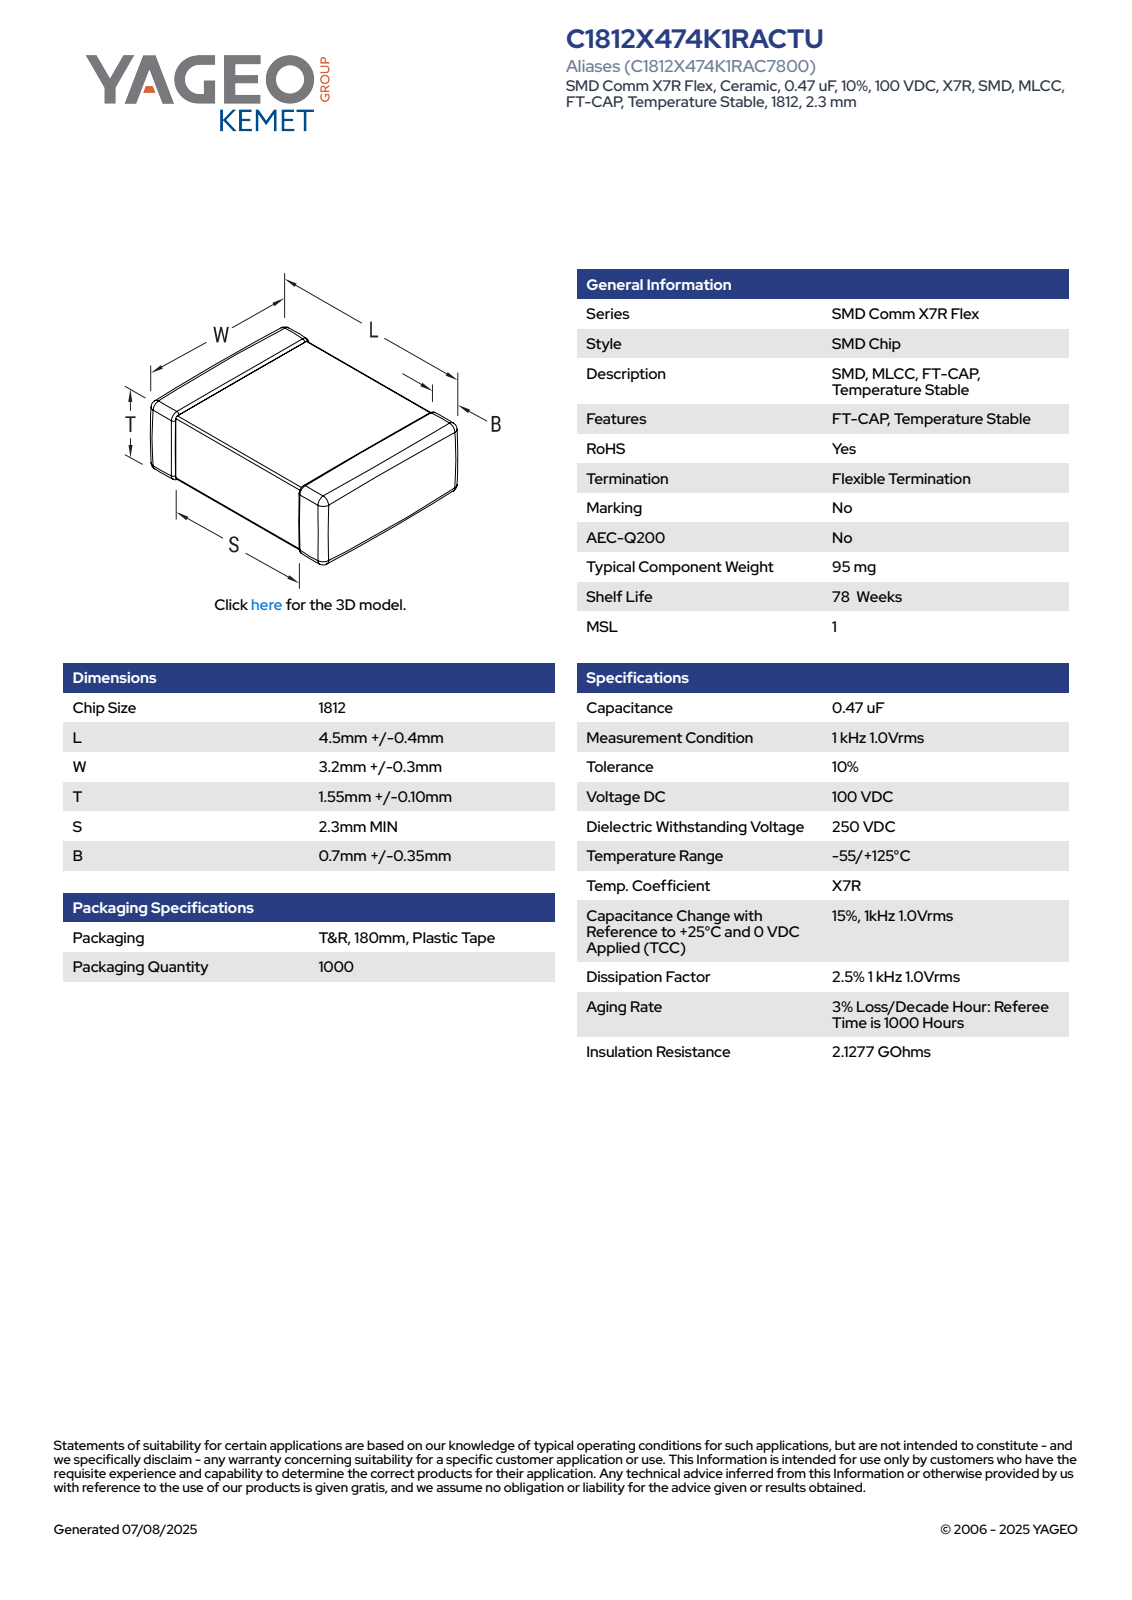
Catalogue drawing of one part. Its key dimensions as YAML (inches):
part_name: "CCS_CCSTD_1812_L4.9W3.5T1.65B0.7"
step_written_by: "SolidWorks 2021 (AUTOMOTIVE_DESIGN)"
units: inches
bodies: {solids: 4, faces: 125, planar: 71, cylindrical: 38, other: 16}
overall_size: [0.193, 0.138, 0.065]
volume: 0.002
surface_area: 0.096
face_to_face_distances: [0.062, 0.059, 0.065, 0.135, 0.193, 0.132, 0.138, 0.02, 0.089, 0.084]
